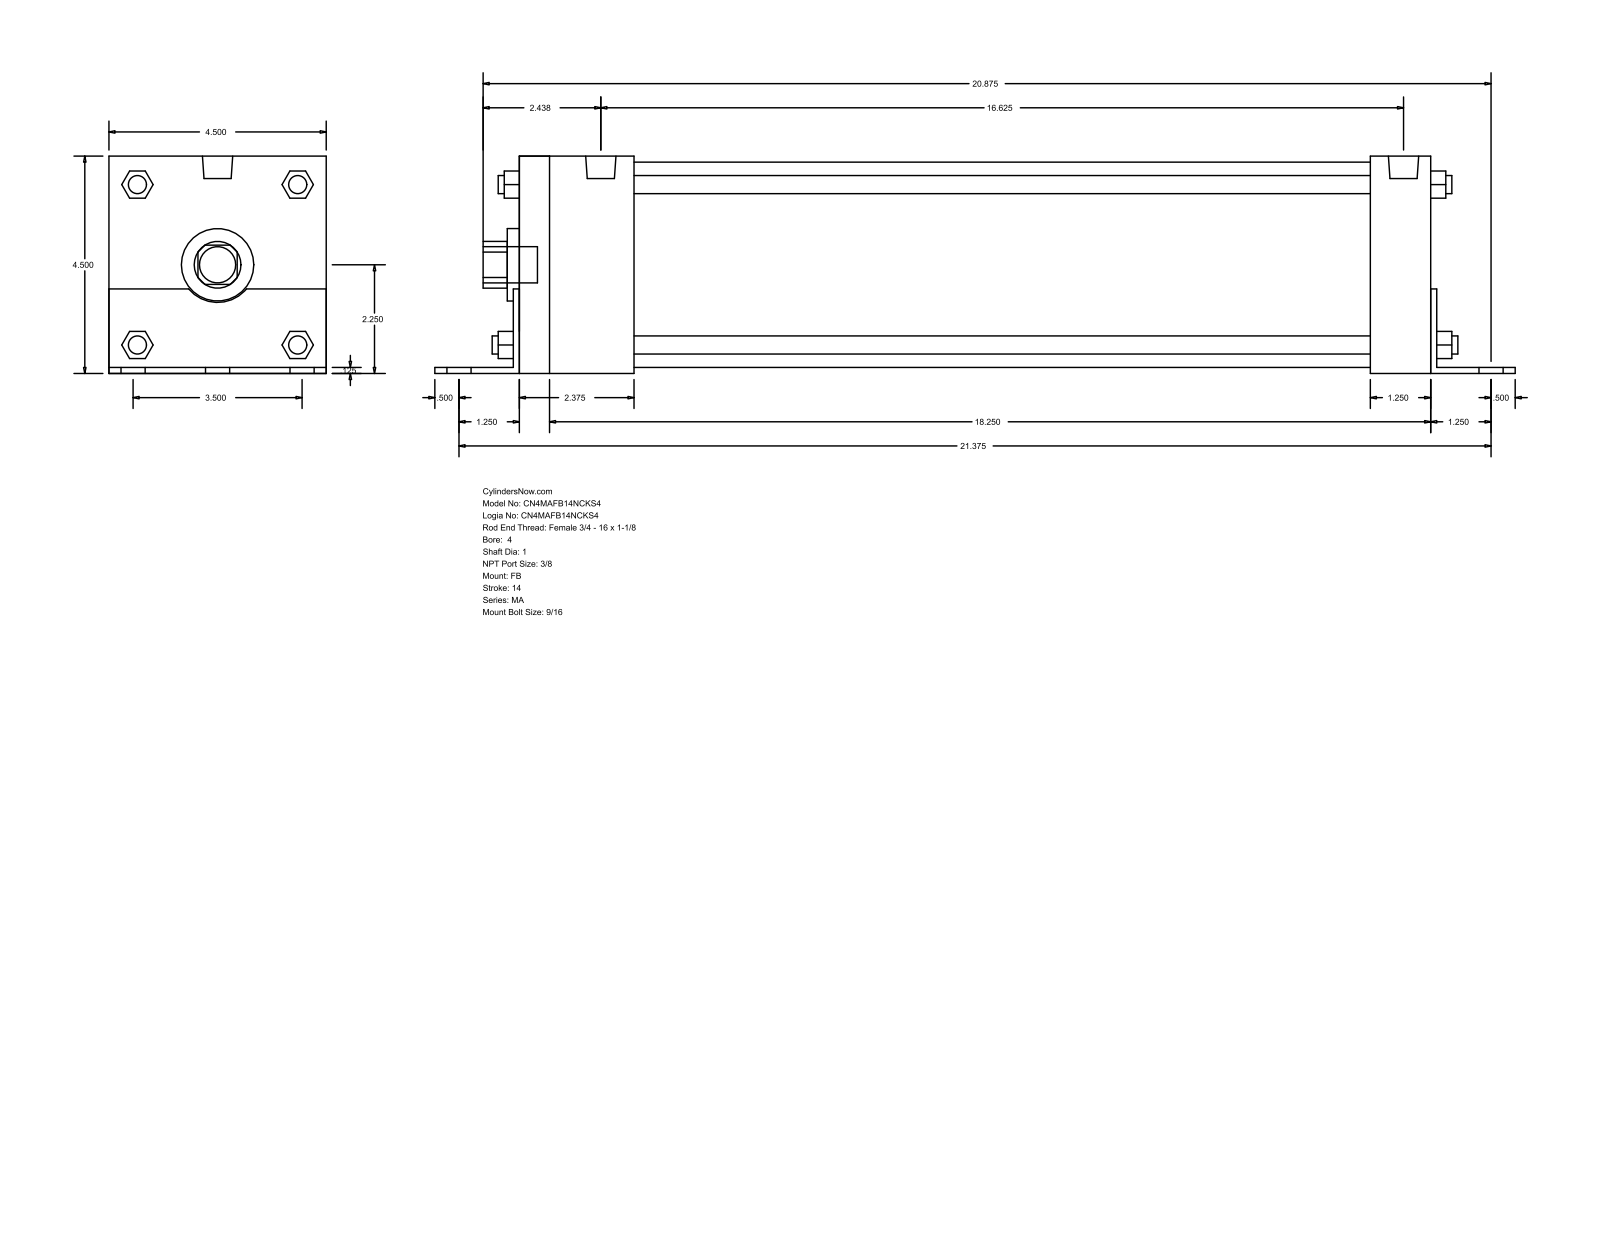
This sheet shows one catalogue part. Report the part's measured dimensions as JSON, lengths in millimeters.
{"part_name": "MA_FB__0400_1", "step_written_by": "GSSL Pune (CONFIG_CONTROL_DESIGN)", "units": "millimeters", "bodies": {"solids": 0, "faces": 140, "planar": 105, "cylindrical": 35, "other": 0}, "overall_size": [568.33, 114.35, 114.3], "round_holes": [[25.4, 1], [38.1, 1], [107.95, 1]], "round_bosses_or_shafts": [[14.29, 6], [11.11, 4], [9.53, 4], [15.93, 2], [19.05, 1]], "partial_cylinders_radius": [[12.29, 1], [19.81, 1]], "face_to_face_distances": [114.3, 3.17, 114.35, 482.6, 3.12, 111.18, 479.43, 485.77, 450.85, 447.68]}
